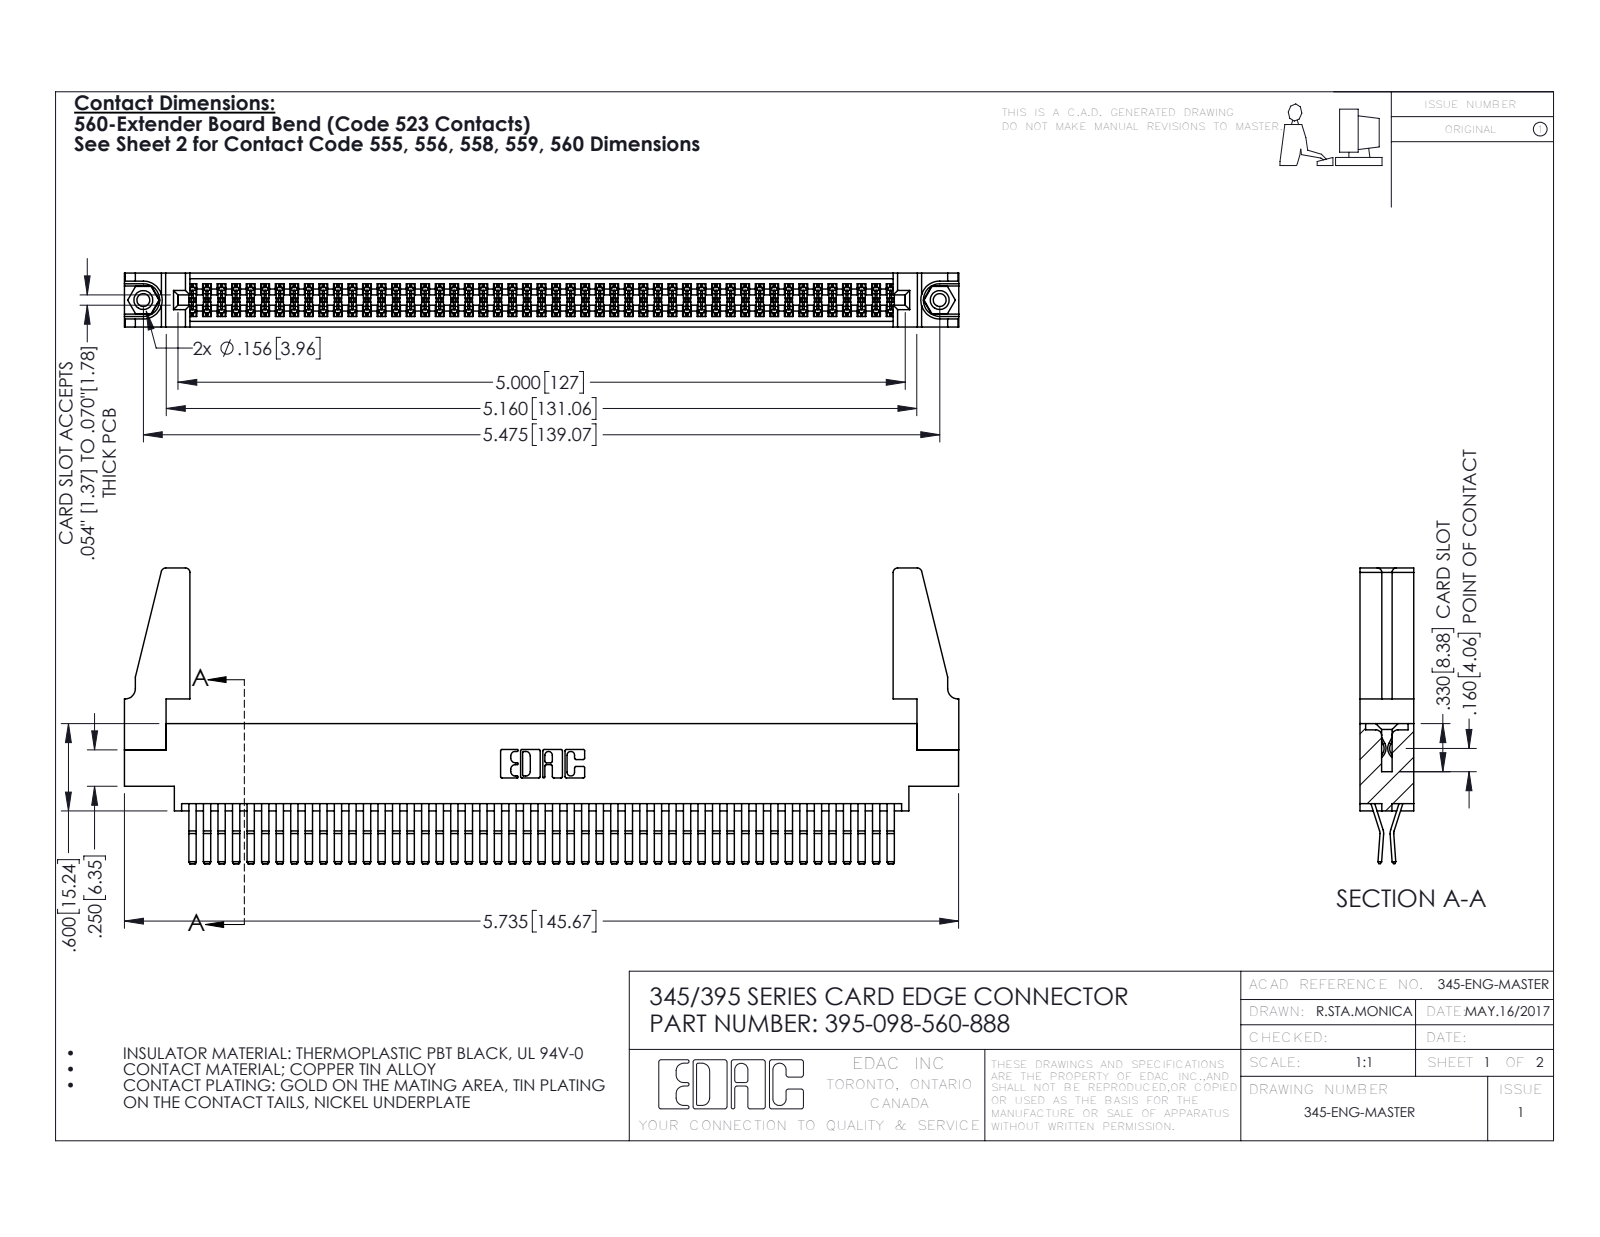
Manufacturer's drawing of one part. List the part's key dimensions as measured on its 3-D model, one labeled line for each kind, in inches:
Part name (STEP PRODUCT): 345-220-078_345-220-088; 345-292-001_560 Tail; 345-250-001_345-250-001-102; 345 Part_0.170 Offset - 0.156 Dia-TH (+1 more)
STEP written by: SolidWorks 2016 (CONFIG_CONTROL_DESIGN)
Units: inches
Bodies: 103 solids, 5350 faces (3390 planar, 1944 cylindrical, 16 other)
Overall size (bounding box): 5.736 × 2.032 × 0.37
Volume: 1.098 in³ · Surface area: 41.62 in²
Round holes (diameter × count): ⌀0.089 ×2, ⌀0.125 ×2, ⌀0.156 ×2, ⌀0.064 ×1
Round bosses / shafts (diameter × count): ⌀0.155 ×2
Partial cylindrical surfaces — rounded edges, fillets, slot ends (radius × count): R0.006 ×147, R0.01 ×22, R0.03 ×8, R0.007 ×6, R0.031 ×6, R0.026 ×3, R0.01 ×2, R0.014 ×2
Main face-to-face distances: 0.072, 0.298, 0.025, 0.37, 0.098, 0.272, 0.2, 0.225, 0.175, 0.149
Hole centre spacings: 0.27, 5.239, 5.475
